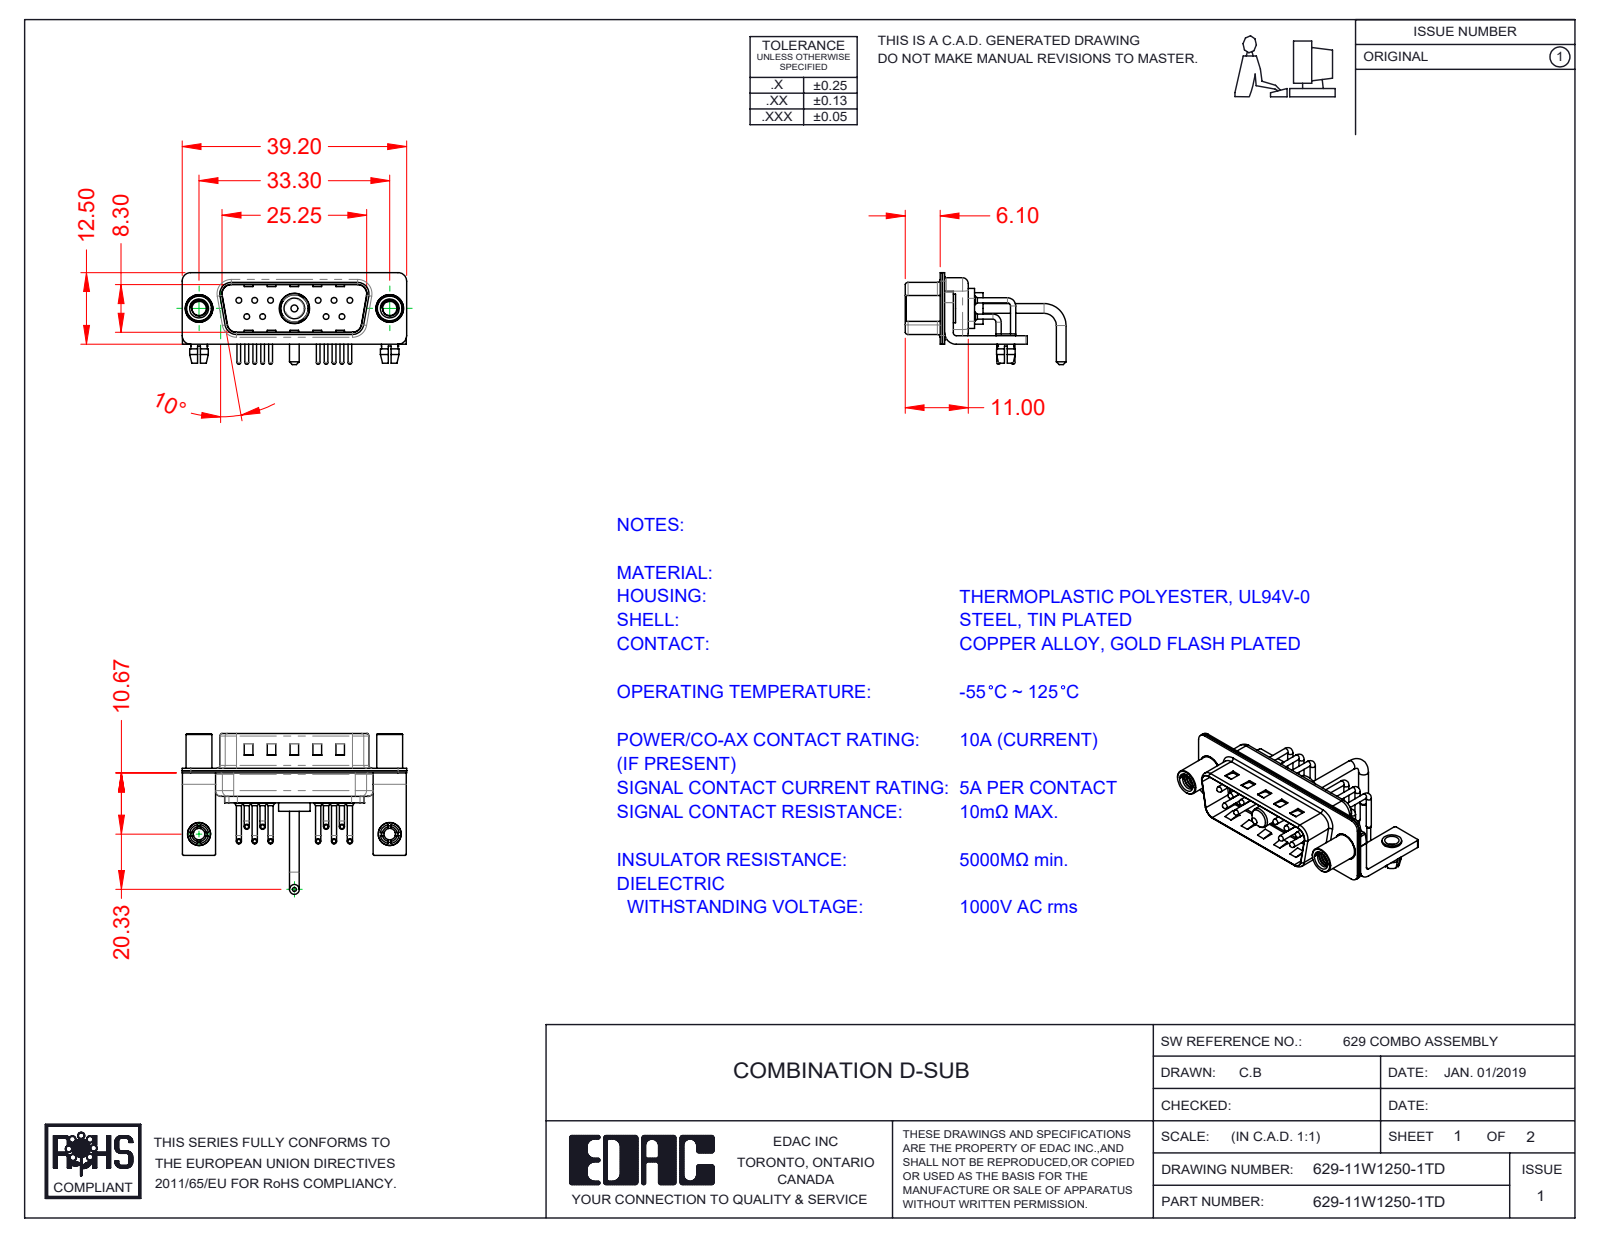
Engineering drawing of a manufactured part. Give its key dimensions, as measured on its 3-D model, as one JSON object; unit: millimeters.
{"part_name": "629Combo Contact Row 1; 629Combo Shell Rear_15 Contacts; 629Combo Housing_11W1; 629-11W1250-1TD (+6 more)", "step_written_by": "SolidWorks 2020 (CONFIG_CONTROL_DESIGN)", "units": "millimeters", "bodies": {"solids": 21, "faces": 1686, "planar": 868, "cylindrical": 622, "other": 196}, "overall_size": [39.2, 28.08, 16.05], "volume_mm3": 2441, "surface_area_mm2": 6355, "round_holes": [[2, 12], [0.75, 10], [1.6, 10], [2.5, 4], [3.2, 2], [4, 2], [4.8, 2], [4.85, 1], [5.3, 1]], "round_bosses_or_shafts": [[0.9, 20], [1.5, 10], [1, 10], [0.65, 10], [5, 2], [4.9, 2], [4.5, 2], [4, 2]], "partial_cylinders_radius": [[0.25, 16], [1.5, 16], [2, 13], [1.01, 10], [0.5, 9], [1.6, 8], [1, 7], [0.6, 4]], "face_to_face_distances": [0.4, 0.8, 1.5, 9.5, 9.1, 8.7, 9.9, 0.6, 1.9, 5.2], "hole_center_spacings": [3.16, 2.77, 13.85, 11.08, 16.62, 5.03, 5.04, 5.54]}
